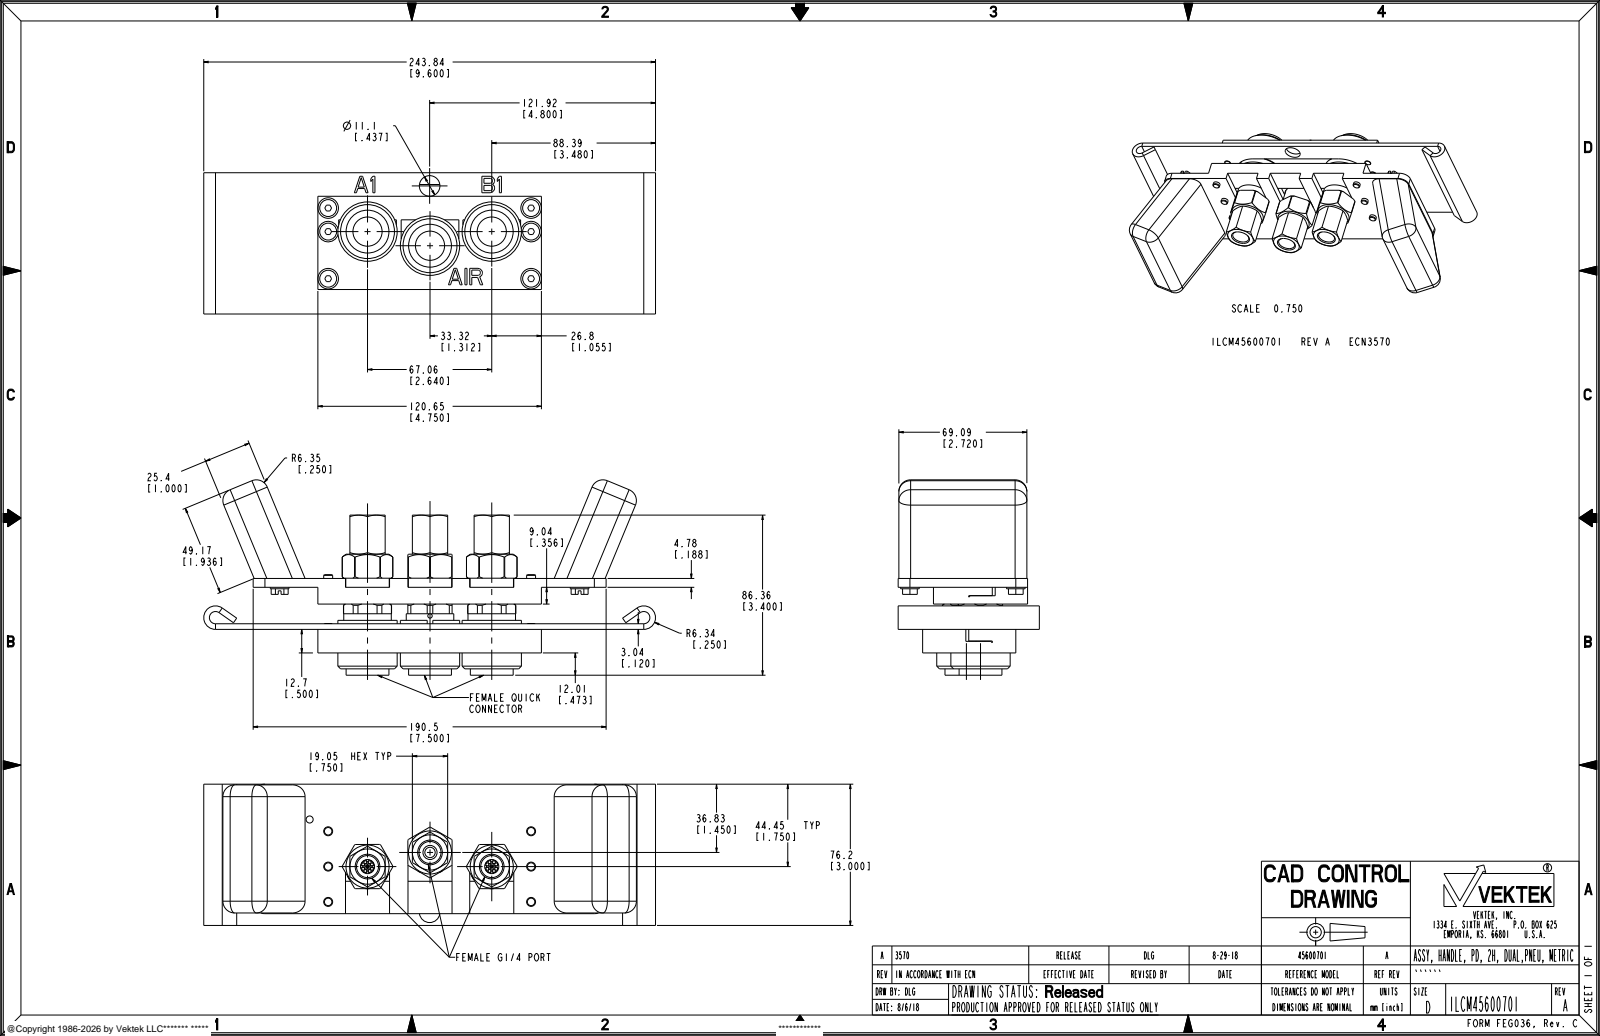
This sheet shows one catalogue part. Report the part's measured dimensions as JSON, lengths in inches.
{"part_name": "ILCM45600701", "step_written_by": "PRO/ENGINEER BY PARAMETRIC TECHNOLOGY CORPORATION, 2013320 (CONFIG_CONTROL_DESIGN)", "units": "inches", "bodies": {"solids": 3, "faces": 1351, "planar": 687, "cylindrical": 464, "other": 200}, "overall_size": [9.6, 4.149, 3], "volume_in3": 30, "surface_area_in2": 232.2, "round_holes": [[0.062, 64], [0.219, 10], [0.264, 4], [0.094, 3], [0.22, 3], [0.3, 3], [0.468, 3], [0.509, 3], [0.62, 3], [0.942, 3], [1.06, 3], [1.226, 3]], "round_bosses_or_shafts": [[0.19, 10], [0.396, 4], [1.26, 3], [1.195, 3], [1.01, 3], [0.923, 3], [0.91, 3], [0.5, 2]], "partial_cylinders_radius": [[0.031, 40], [0.25, 20], [0.059, 3], [0.468, 3], [0.511, 3], [0.537, 3], [0.68, 3], [0.13, 2]], "face_to_face_distances": [0.12, 0.894, 0.774, 1.081, 0.962, 0.188, 0.5, 1, 0.356, 0.538], "hole_center_spacings": [0.194, 0.274, 0.332, 4.312, 0.2, 0.25, 0.274, 0.75]}
